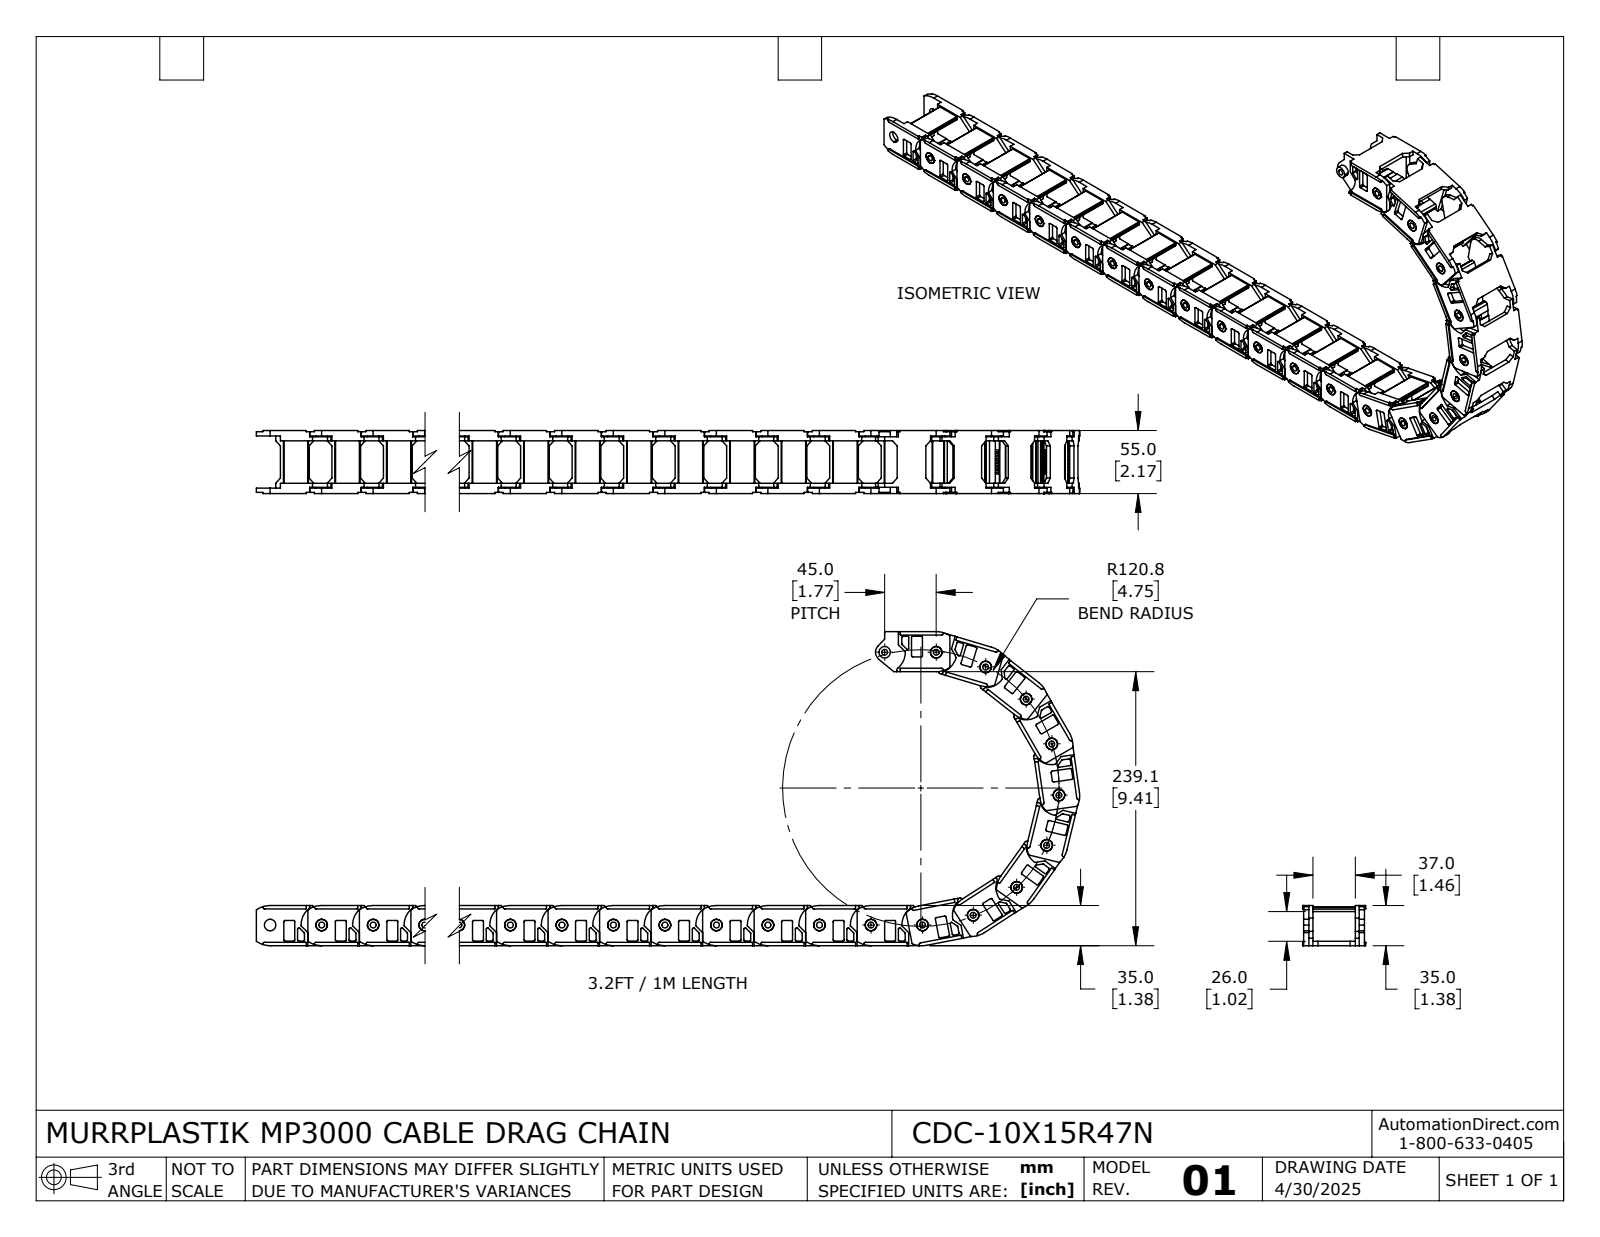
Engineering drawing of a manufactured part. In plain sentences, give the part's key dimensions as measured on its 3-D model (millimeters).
The part is named "CDC-10X15R47N". Its 3-D file was written by "SolidWorks 2024 (AUTOMOTIVE_DESIGN)". It is 22 solids with 3696 faces: 2596 planar, 1100 cylindrical and 0 other. Overall it measures 734.02 by 274.11 by 55 millimeters. Its volume is 587 391 cubic millimeters and its surface area 349 280 square millimeters. Round holes: 22 of diameter 5.1, 22 of diameter 10.1. Round bosses or shafts: 22 of diameter 10. Partial cylindrical surfaces (rounded edges, fillets, slot ends): 176 of radius 1, 88 of radius 0.5, 44 of radius 1.5, 44 of radius 2, 44 of radius 21, 22 of radius 2.8, 22 of radius 8, 22 of radius 18. The main face-to-face distances are 45, 8, 4, 3.7, 49.3, 4.3, 41.3, 37, 3.5, 0.8. The hole center spacings are 44.98, 45, 89.96, 134.94, 89.98, 164.42, 179.92, 44.96.
